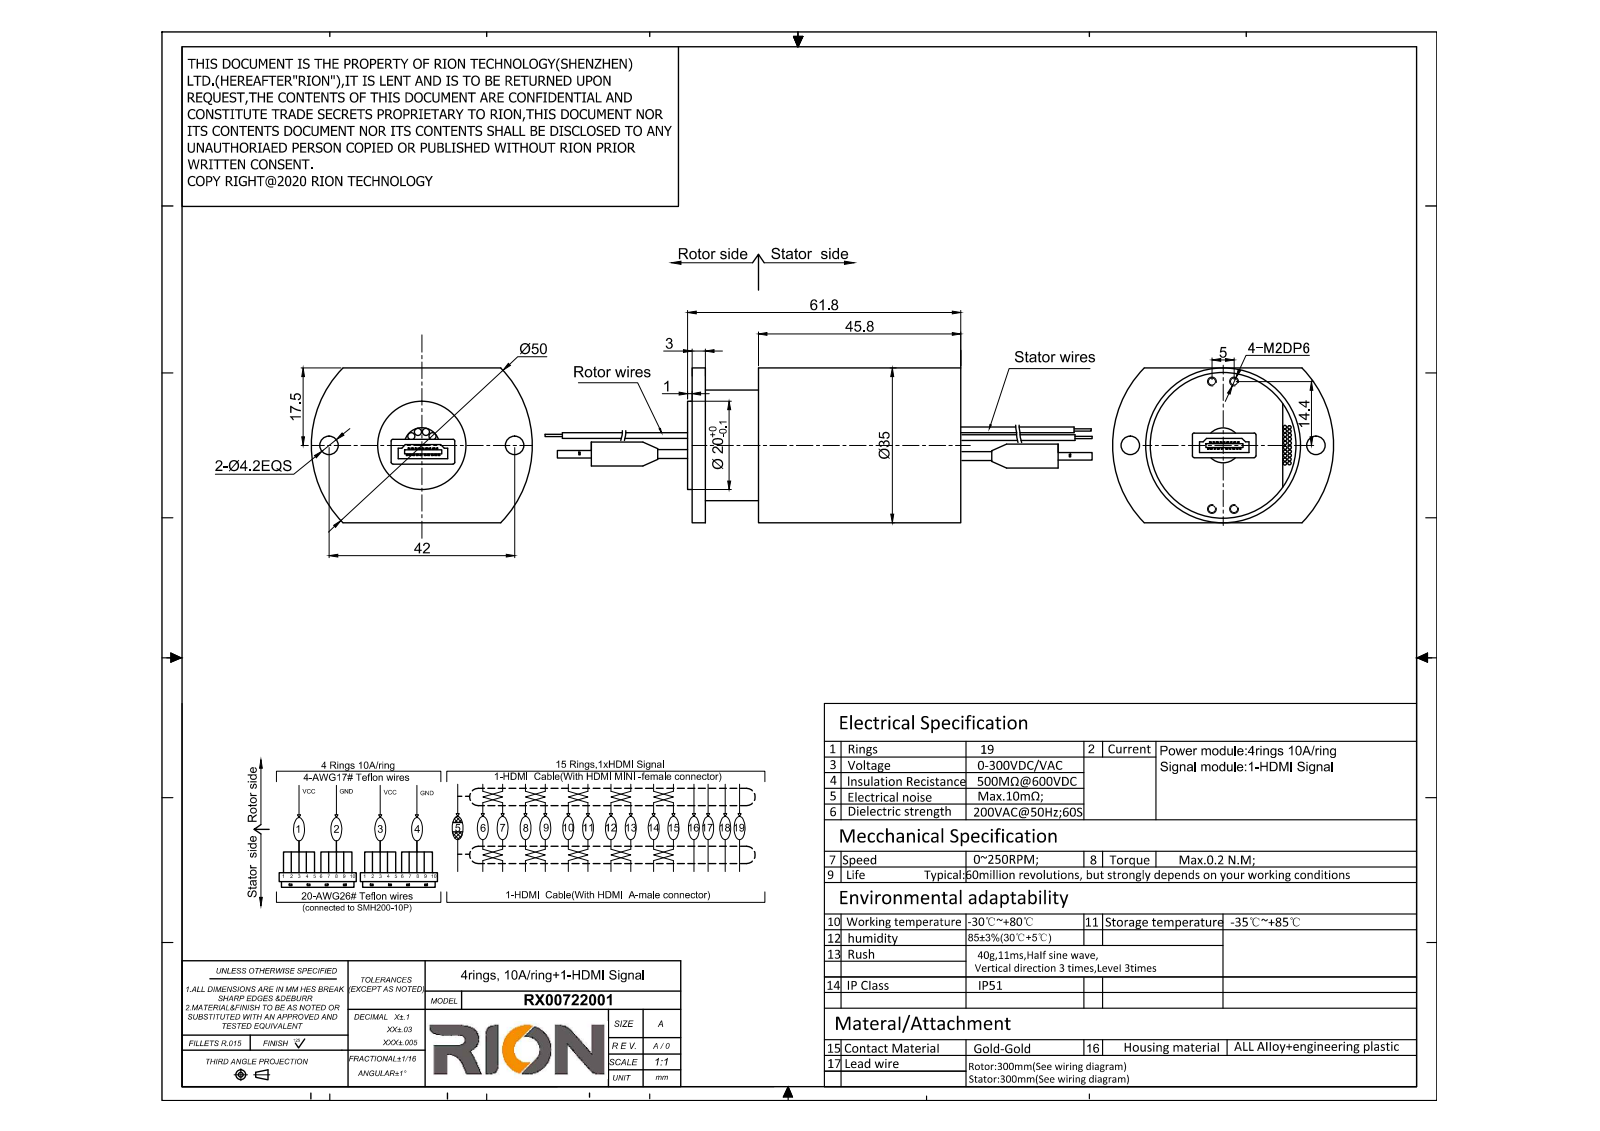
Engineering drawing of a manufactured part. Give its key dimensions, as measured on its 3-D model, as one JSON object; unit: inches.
{"part_name": "RX00722001-- RGZ035-P0410-1HDMI", "step_written_by": "SolidWorks 2014 (CONFIG_CONTROL_DESIGN)", "units": "inches", "bodies": {"solids": 1, "faces": 122, "planar": 37, "cylindrical": 77, "other": 8}, "overall_size": [3.181, 1.969, 1.378], "volume_in3": 3.381, "surface_area_in2": 18.54, "round_holes": [[0.063, 4], [0.165, 2], [0.311, 1], [0.315, 1], [1.303, 1]], "round_bosses_or_shafts": [[0.031, 18], [0.063, 4], [0.197, 2], [1.378, 1], [1.299, 1], [0.984, 1], [0.787, 1]], "partial_cylinders_radius": [[0.984, 1]], "face_to_face_distances": [0.118, 2.394, 2.276, 1.803, 0.472, 0.591, 0.039, 2.433, 0.63, 0.157], "hole_center_spacings": [0.576, 0.923, 1.085, 0.197, 0.827, 1.134, 1.151, 1.654]}
